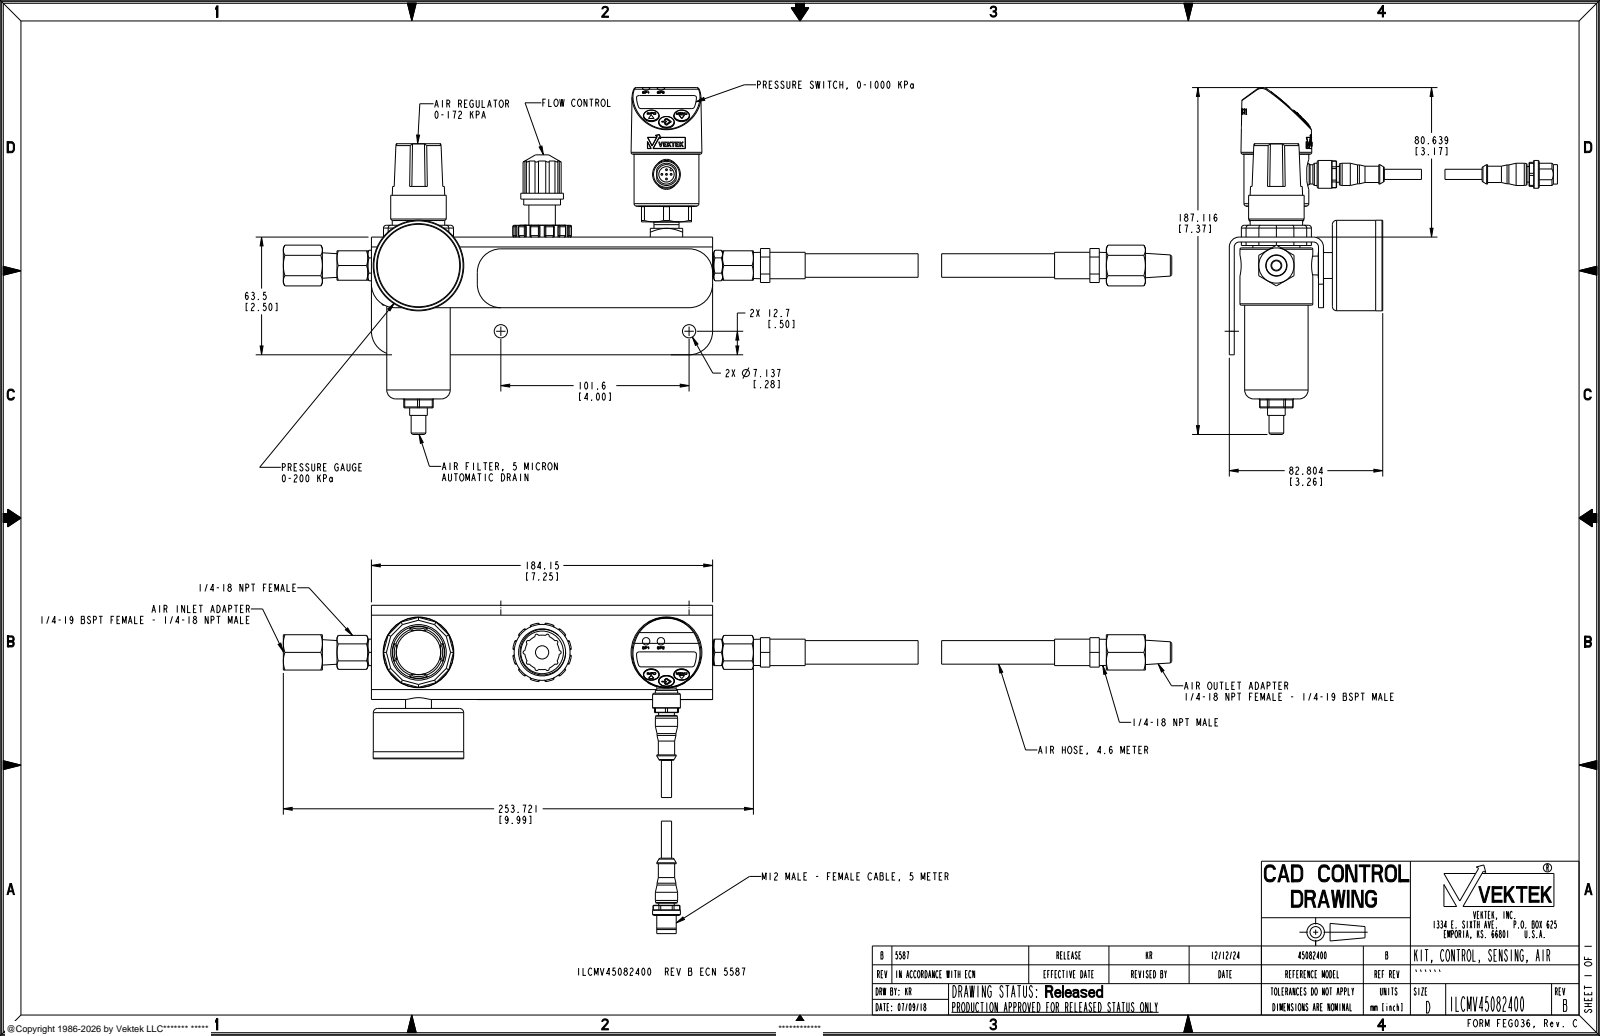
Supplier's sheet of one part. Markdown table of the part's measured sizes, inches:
| quantity | value |
| --- | --- |
| part name | ILCMV45082400 |
| STEP written by | CREO PARAMETRIC BY PTC INC, 2021164 (AUTOMOTIVE_DESIGN) |
| units | inches |
| bodies | 11 solids, 1872 faces (558 planar, 378 cylindrical, 936 other) |
| overall size | 18.879 × 7.367 × 6.972 |
| volume | 24.82 in³ |
| surface area | 211.4 in² |
| round holes (diameter × count) | 0.281 × 2, 0.437 × 2, 1 × 2, 1.125 × 2, 0.043 × 1, 0.13 × 1, 0.136 × 1, 0.138 × 1, 0.2 × 1, 0.219 × 1, 0.23 × 1, 0.327 × 1 |
| round bosses / shafts (diameter × count) | 0.039 × 5, 0.375 × 2, 1.925 × 1, 1.92 × 1, 1.548 × 1, 1.378 × 1, 1.348 × 1, 1.189 × 1 |
| partial cylindrical surfaces (radius × count) | 0.015 × 48, 0.02 × 12, 0.06 × 12, 0.037 × 10, 0.062 × 8, 0.5 × 7, 0.004 × 6, 0.04 × 6 |
| main face-to-face distances | 0.105, 1.895, 1.79, 2.002, 1.897, 0.107, 0.656, 0.812, 0.625, 0.031 |
| hole center spacings | 0.02, 0.021, 1, 2.226, 2.239, 2.623, 2.625, 2.625 |
